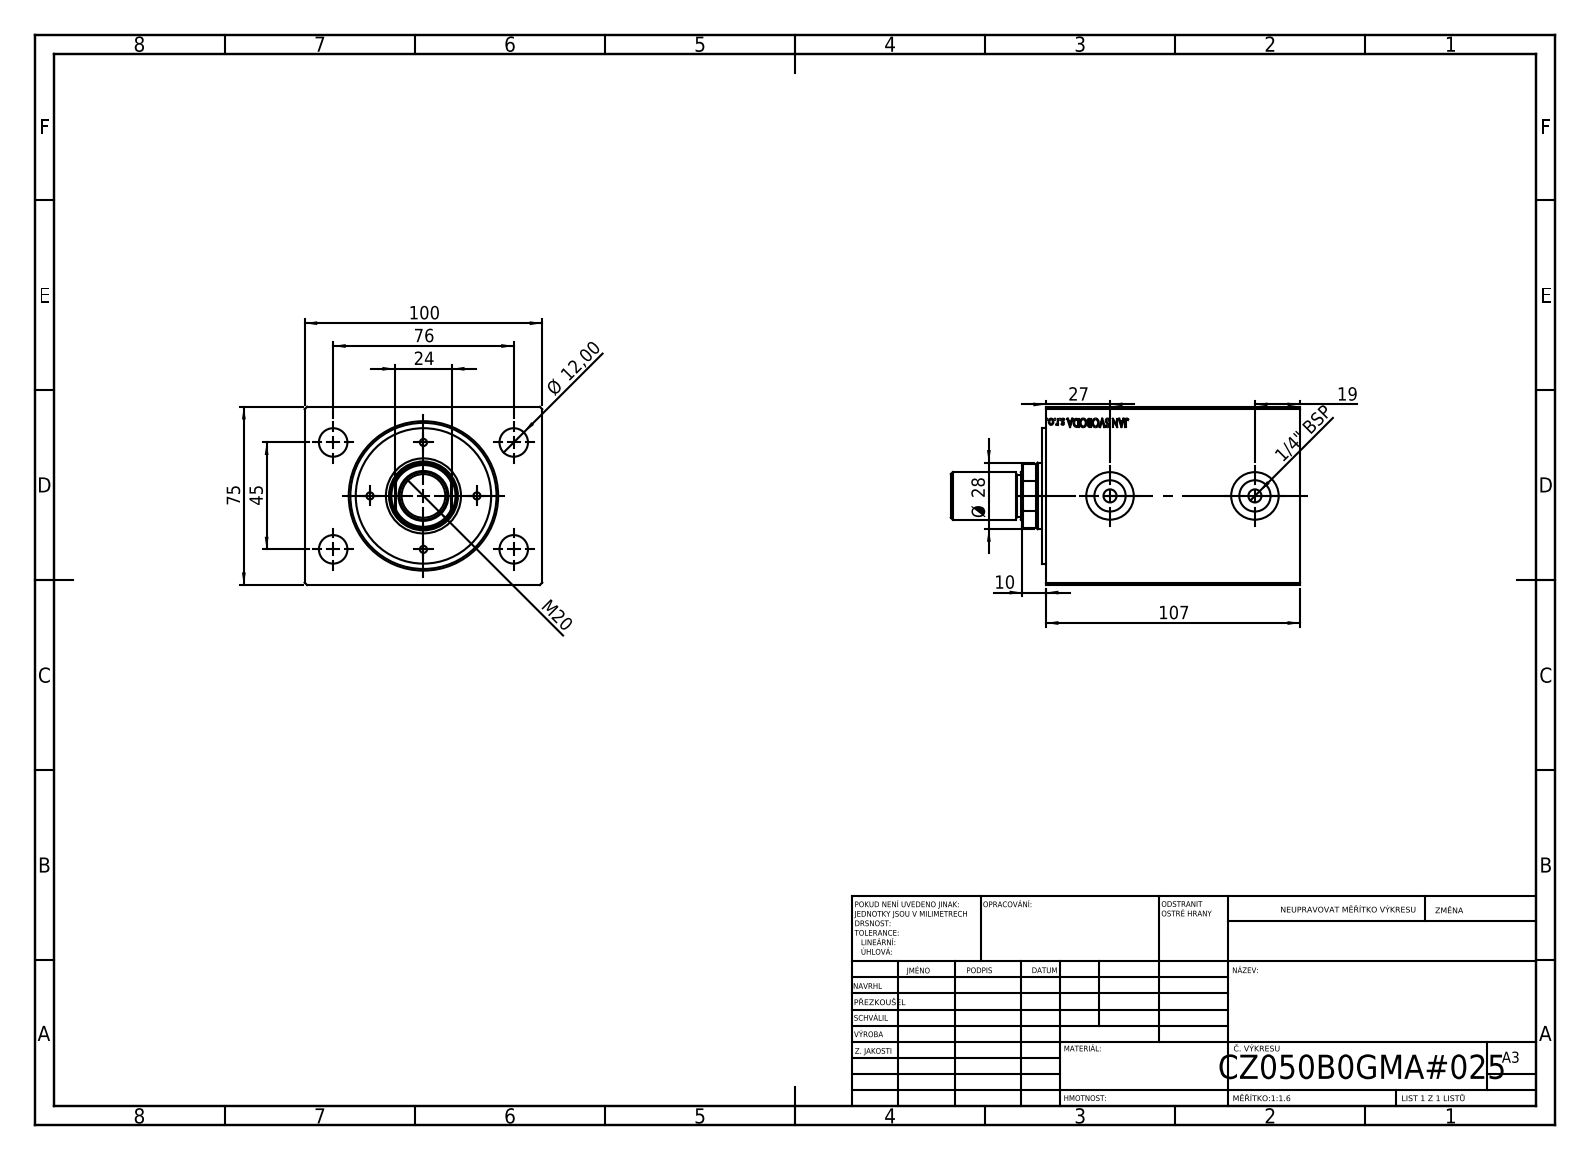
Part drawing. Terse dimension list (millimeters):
name: V500CZ; V500CZ_MALE_METRIC; V500CZ_B_VC
written by: SolidWorks 2019 (CONFIG_CONTROL_DESIGN)
unit: mm
bodies: 4 solids, 888 faces (404 planar, 62 cylindrical, 422 other)
size: 147 × 100 × 75
volume: 746 733 mm³; area: 103 608 mm²
holes: 4× ⌀3, 4× ⌀12, 2× ⌀5.5, 2× ⌀13.16, 2× ⌀20, 1× ⌀18.5, 1× ⌀28, 1× ⌀29, 1× ⌀36, 1× ⌀50, 1× ⌀61.5
bosses: 1× ⌀57, 1× ⌀20, 1× ⌀18
rounds: 1× R13.5
face distances: 75, 100, 107, 89.2, 17.8, 10, 8.2, 1.8, 81, 98.8
hole spacings: 22.5, 27.32, 31.82, 38, 44.16, 45, 58.9, 64.55
